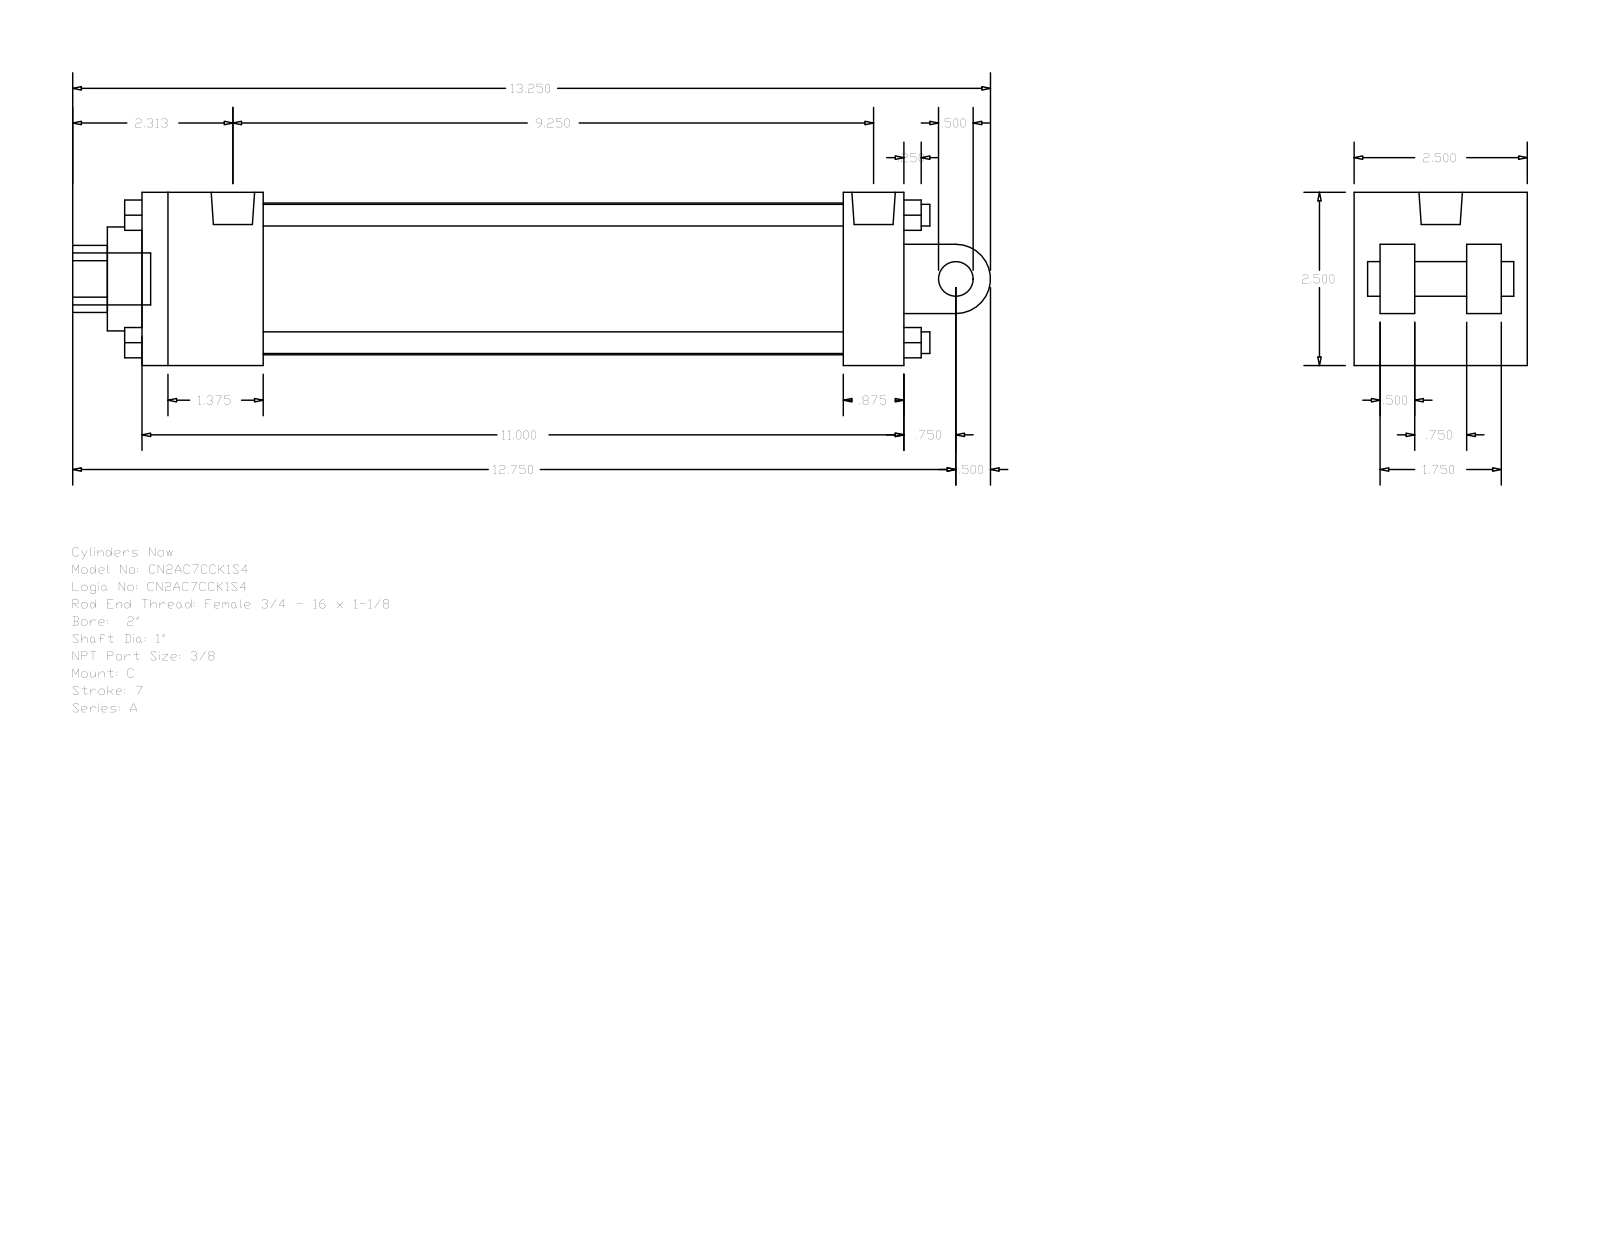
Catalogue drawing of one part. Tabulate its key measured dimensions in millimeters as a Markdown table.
| quantity | value |
| --- | --- |
| part name | A_C__0200_1 |
| STEP written by | GSSL Pune (CONFIG_CONTROL_DESIGN) |
| units | millimeters |
| bodies | 0 solids, 135 faces (102 planar, 33 cylindrical, 0 other) |
| overall size | 336.55 × 63.5 × 63.5 |
| round holes (diameter × count) | 5.56 × 2, 15.93 × 1, 25.4 × 1, 38.1 × 1, 55.63 × 1 |
| round bosses / shafts (diameter × count) | 7.94 × 4, 5.56 × 2, 19.05 × 1, 15.93 × 1, 12.7 × 1 |
| partial cylindrical surfaces (radius × count) | 12.29 × 1, 12.7 × 1 |
| main face-to-face distances | 63.5, 279.4, 44.45, 12.7, 9.52, 41.28, 234.95, 257.17, 212.72, 22.23 |
| hole center spacings | 3.98 |
